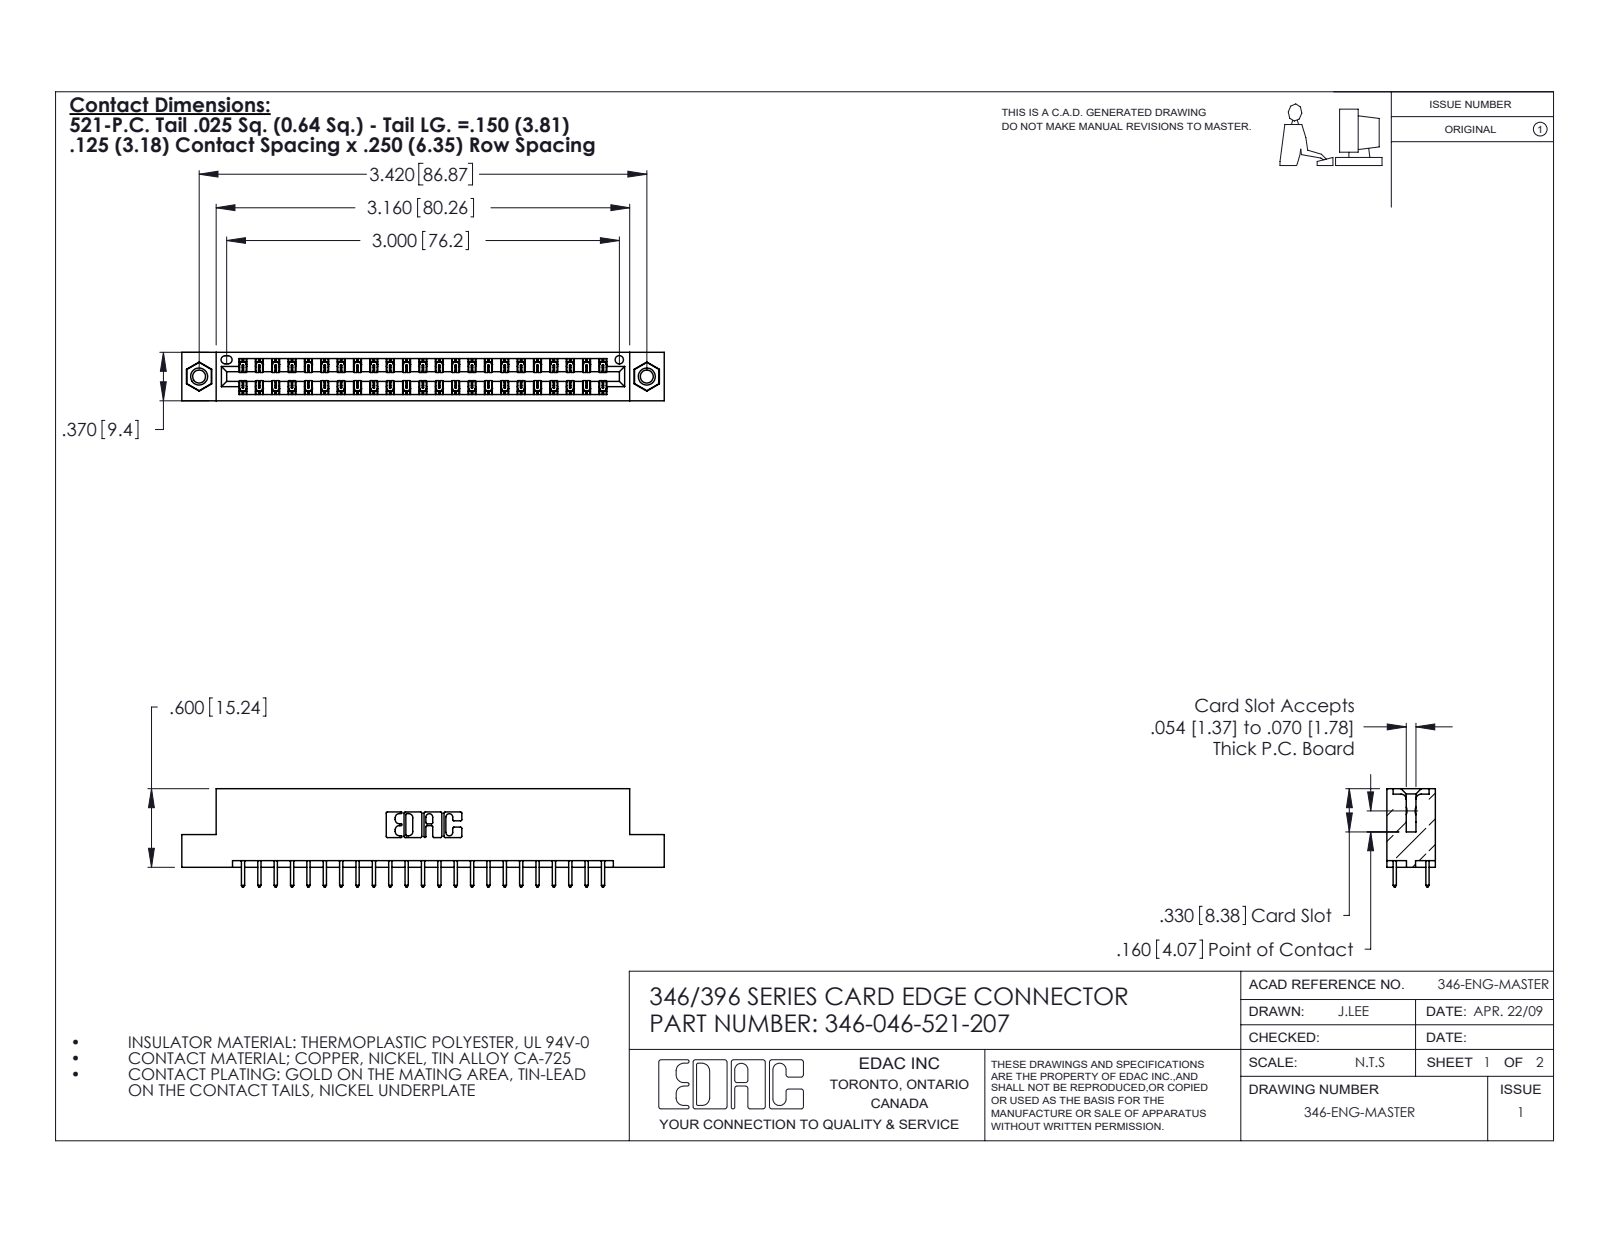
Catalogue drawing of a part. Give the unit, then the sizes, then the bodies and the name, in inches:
Units: inches
Overall size (bounding box): 3.685 × 0.75 × 0.37
Round holes (diameter × count): ⌀0.098 ×2, ⌀0.125 ×2, ⌀0.156 ×2, ⌀0.064 ×1
Round bosses / shafts (diameter × count): ⌀0.155 ×2
Partial cylindrical surfaces — rounded edges, fillets, slot ends (radius × count): R0.006 ×69, R0.01 ×46, R0.01 ×22, R0.007 ×6, R0.031 ×6, R0.026 ×3, R0.014 ×2, R0.022 ×2
Main face-to-face distances: 0.048, 0.322, 0.25, 0.37, 0.072, 0.298, 0.025, 0.275, 0.148, 0.222
Hole centre spacings: 0.246, 3.212, 3.42
Volume: 0.546 in³ · Surface area: 18.46 in²
Bodies: 49 solids, 2574 faces (1718 planar, 840 cylindrical, 16 other)
Part name (STEP PRODUCT): 346 Part_Flush Mounting Lugs - 0.156 Dia-TI; 345-250-001_345-250-005-103; 346-046-521-207; 345-292-001_345-293-121
STEP written by: SolidWorks 2020 (CONFIG_CONTROL_DESIGN)
